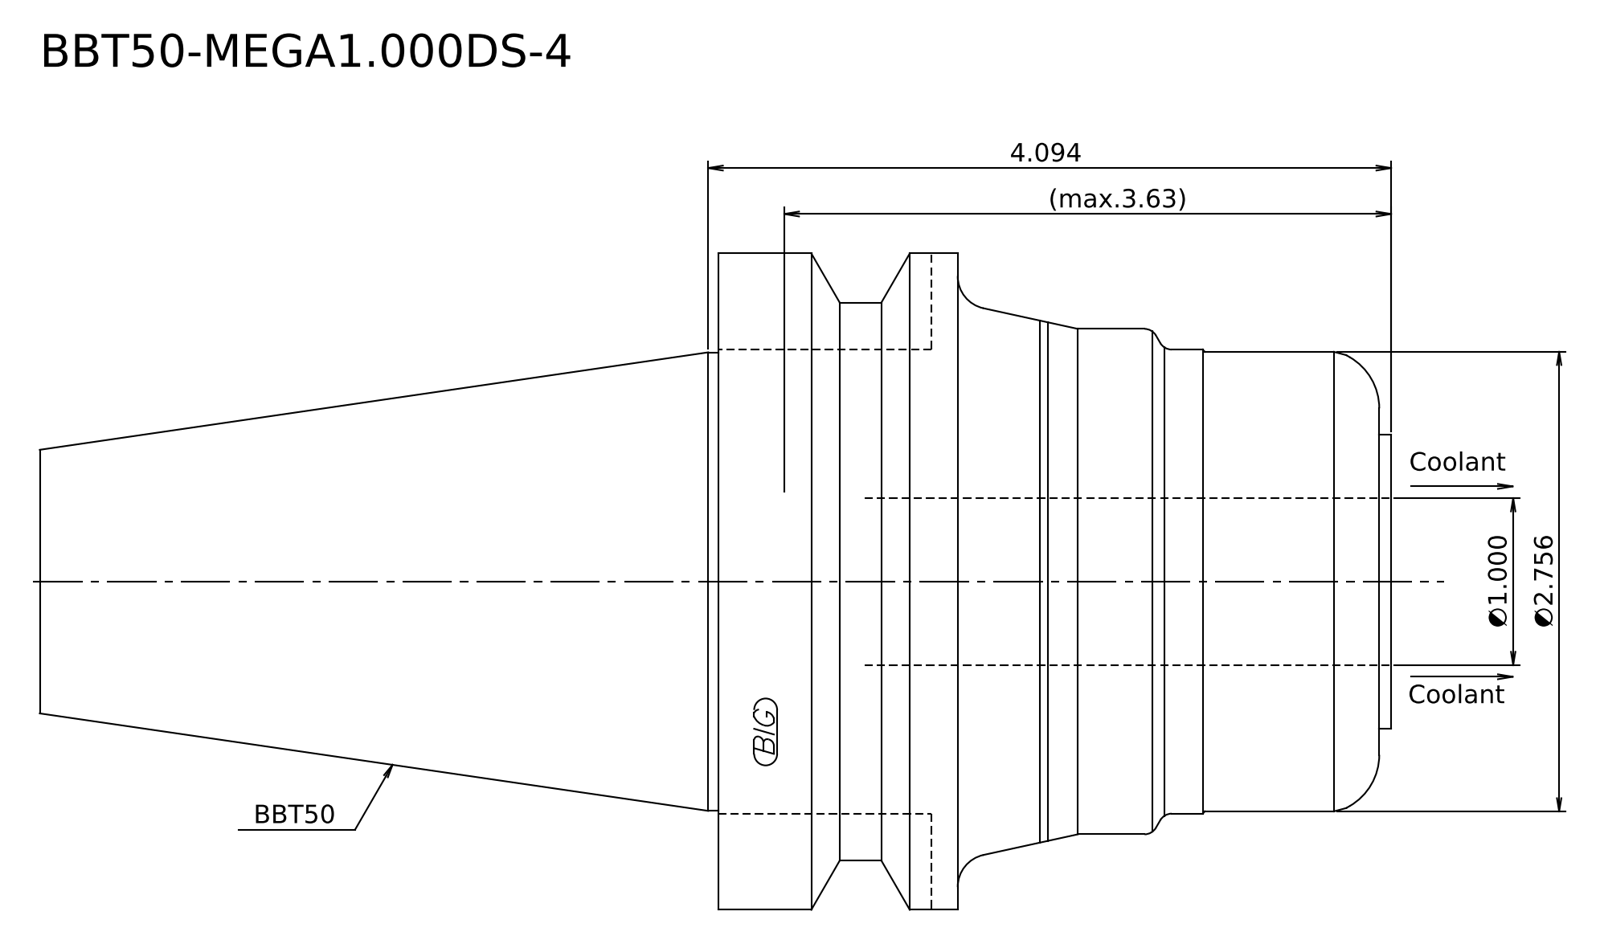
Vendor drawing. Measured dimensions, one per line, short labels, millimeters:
written by: Kubotek KeyCreator 2011 V10.0.2 (22737) (automotive_design)
unit: mm
bodies: 1 solid, 22 faces (5 planar, 8 cylindrical, 9 other)
size: 205.8 × 100 × 100
volume: 800 816 mm³; area: 57 570 mm²
bosses: 1× ⌀100, 1× ⌀85, 1× ⌀77, 1× ⌀70.7, 1× ⌀70, 1× ⌀69.85, 1× ⌀44.77
face distances: 102.5, 1.8, 100.7, 205.8, 204, 103.3, 66, 64.2, 36.5, 139.8
